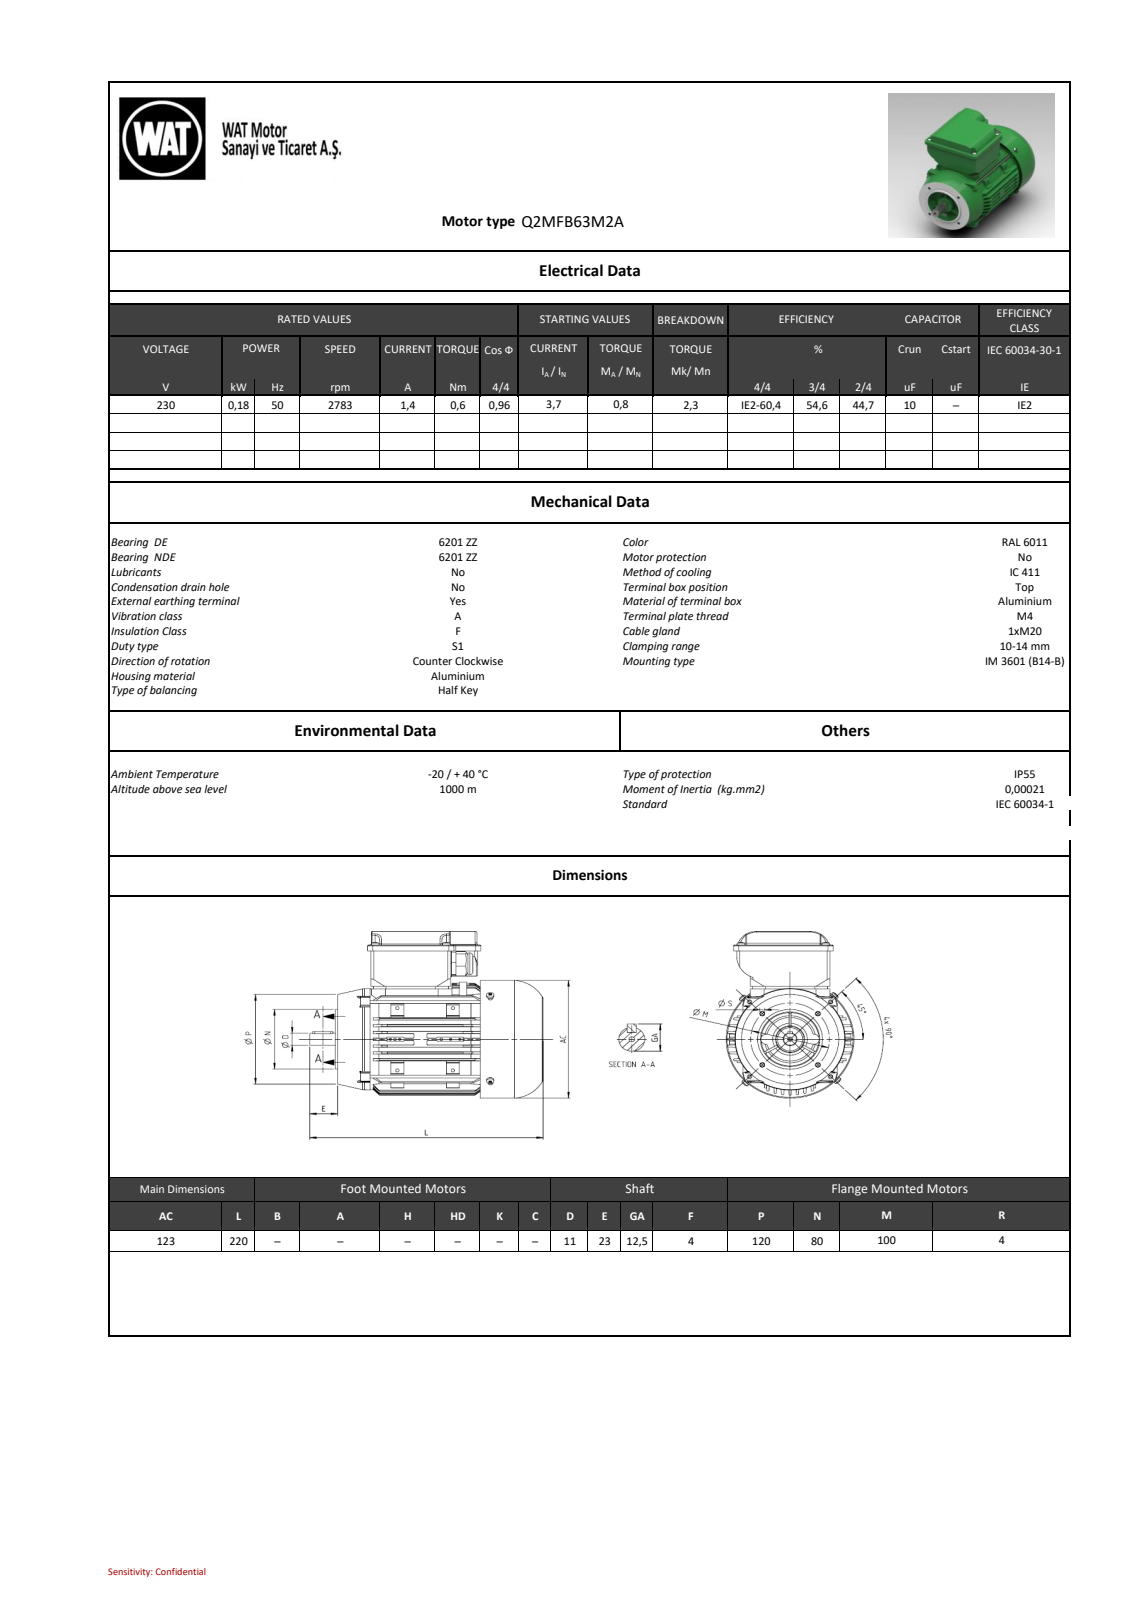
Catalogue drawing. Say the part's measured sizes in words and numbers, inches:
The part is named "BY6424130xx_004-TKK_QM63-80; BY6434017xx_004-TK_QM63-80; BY6424189xx_005-MOTOR_KAPAGI_QS63FB_ISLEME; BY6423003xx_006-FAN_KAPAGI_QS63 (+7 more)". Its 3-D file was written by "SIEMENS PLM Software NX2206.8101 (AUTOMOTIVE_DESIGN)". It is 34 solids with 2220 faces: 1135 planar, 758 cylindrical and 327 other. Overall it measures 8.641 by 7.087 by 4.843 inches. Its volume is 36.58 cubic inches and its surface area 629 square inches. Round holes: 10 of diameter 0.144, 8 of diameter 0.177, 6 of diameter 0.098, 5 of diameter 0.13, 4 of diameter 0.138, 4 of diameter 0.157, 4 of diameter 0.183, 4 of diameter 0.189, 4 of diameter 0.236, 3 of diameter 0.118, 1 of diameter 0.197, 1 of diameter 0.315. Round bosses or shafts: 8 of diameter 0.315, 8 of diameter 0.157, 8 of diameter 0.118, 1 of diameter 4.843, 1 of diameter 4.724, 1 of diameter 3.15, 1 of diameter 2.756, 1 of diameter 1.181. Partial cylindrical surfaces (rounded edges, fillets, slot ends): 210 of radius 0.02, 92 of radius 0.039, 79 of radius 0.079, 21 of radius 0.118, 20 of radius 0.098, 10 of radius 0.197, 9 of radius 0.217, 8 of radius 0.059. The main face-to-face distances are 0.118, 0.276, 1.101, 0.177, 0.276, 0.059, 0.098, 1.104, 0.157, 0.271. The hole center spacings are 2.165, 2.144, 3.031, 2.126, 2.48, 2.634, 2.784, 3.267.
